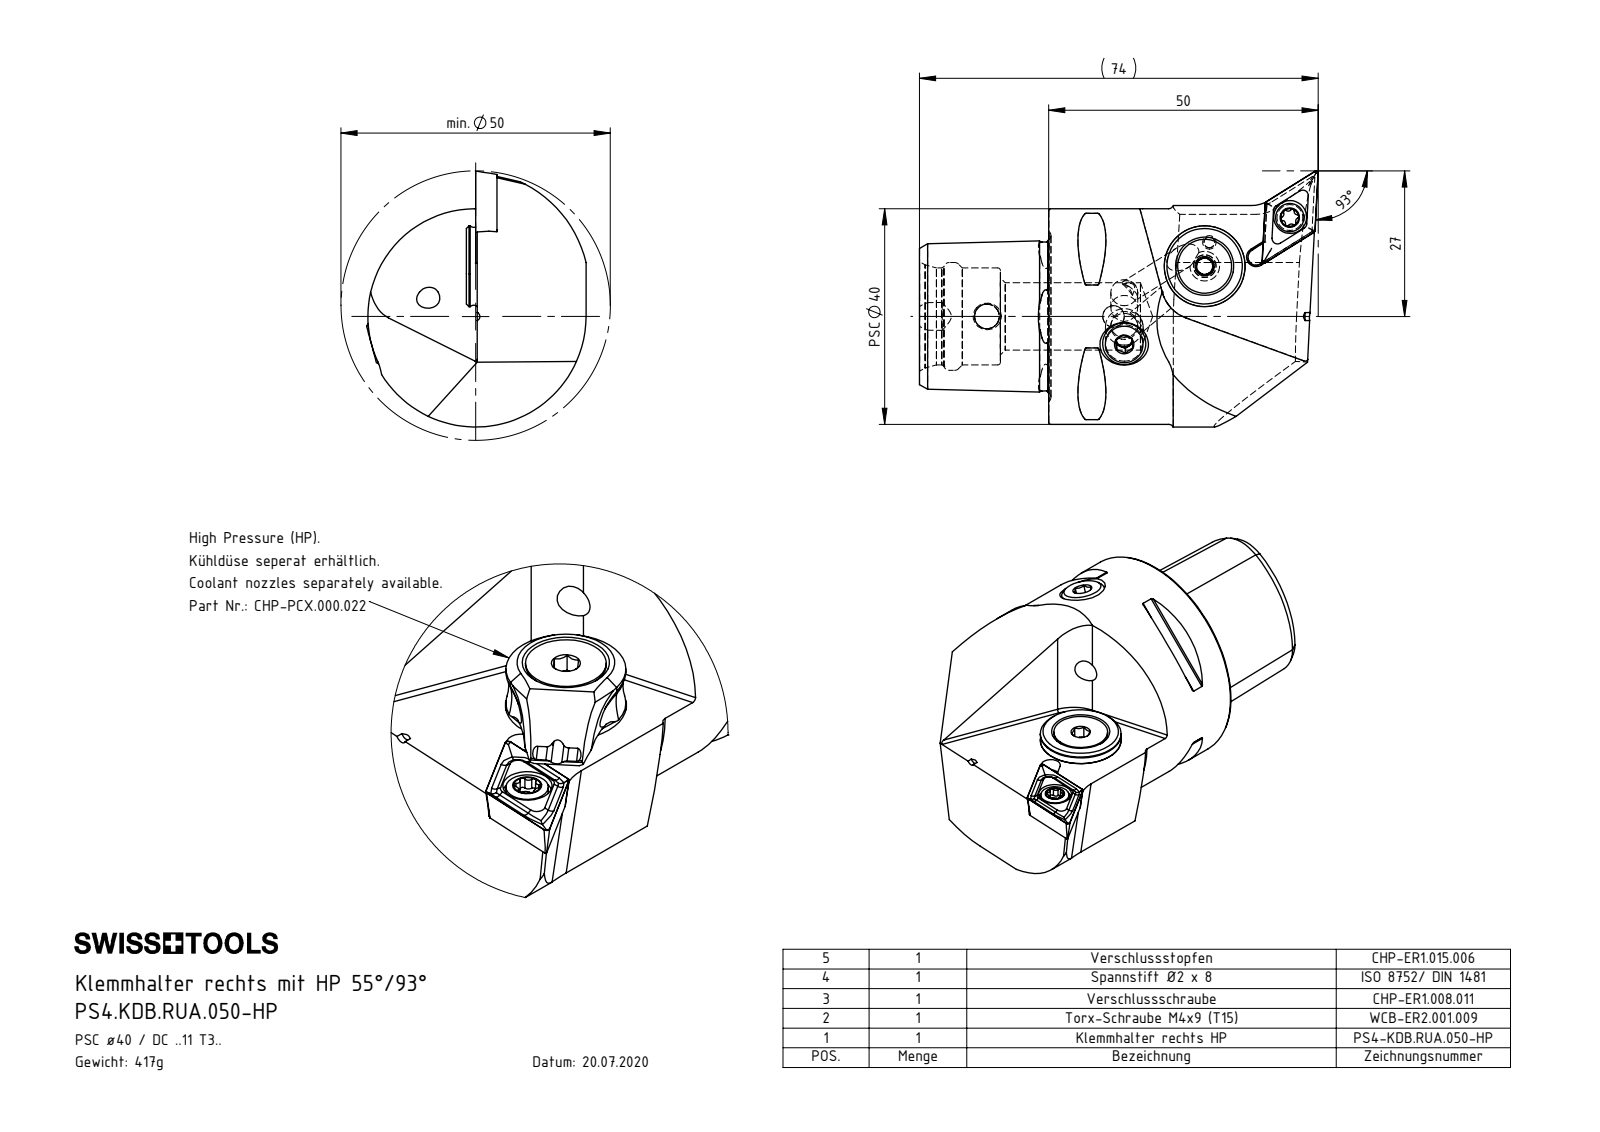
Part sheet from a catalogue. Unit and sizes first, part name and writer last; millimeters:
Units: millimetres
Overall size (bounding box): 74 × 47.51 × 40.72
Round holes (diameter × count): ⌀4.2 ×3, ⌀1.2 ×1, ⌀2 ×1, ⌀2.5 ×1, ⌀3 ×1, ⌀3.3 ×1, ⌀4 ×1, ⌀4.4 ×1, ⌀4.6 ×1, ⌀5 ×1, ⌀5.2 ×1, ⌀6.1 ×1
Round bosses / shafts (diameter × count): ⌀40 ×1, ⌀15 ×1, ⌀13.4 ×1, ⌀10 ×1, ⌀8 ×1, ⌀5.5 ×1, ⌀5.25 ×1, ⌀5 ×1
Partial cylindrical surfaces — rounded edges, fillets, slot ends (radius × count): R0.3 ×8, R0.34 ×6, R0.59 ×6, R0.5 ×2, R7 ×2, R0.8 ×1, R1.5 ×1, R3 ×1
Main face-to-face distances: 4.5, 15.7, 20.2, 24, 16.53, 0.83, 3.67, 15.52, 35.3, 15
Hole centre spacings: 4.5, 15.64, 15.73, 18.21, 18.31, 19.33, 22.48, 23.5
Volume: 53 200 mm³ · Surface area: 15 712 mm²
Bodies: 8 solids, 389 faces (91 planar, 101 cylindrical, 197 other)
Part name (STEP PRODUCT): DCMT11T304; DIN 3771 - 13x1; CHP-ER1.015.006; CHP-ER1.008.011_A (+6 more)
STEP written by: SolidWorks 2017 (AUTOMOTIVE_DESIGN)
